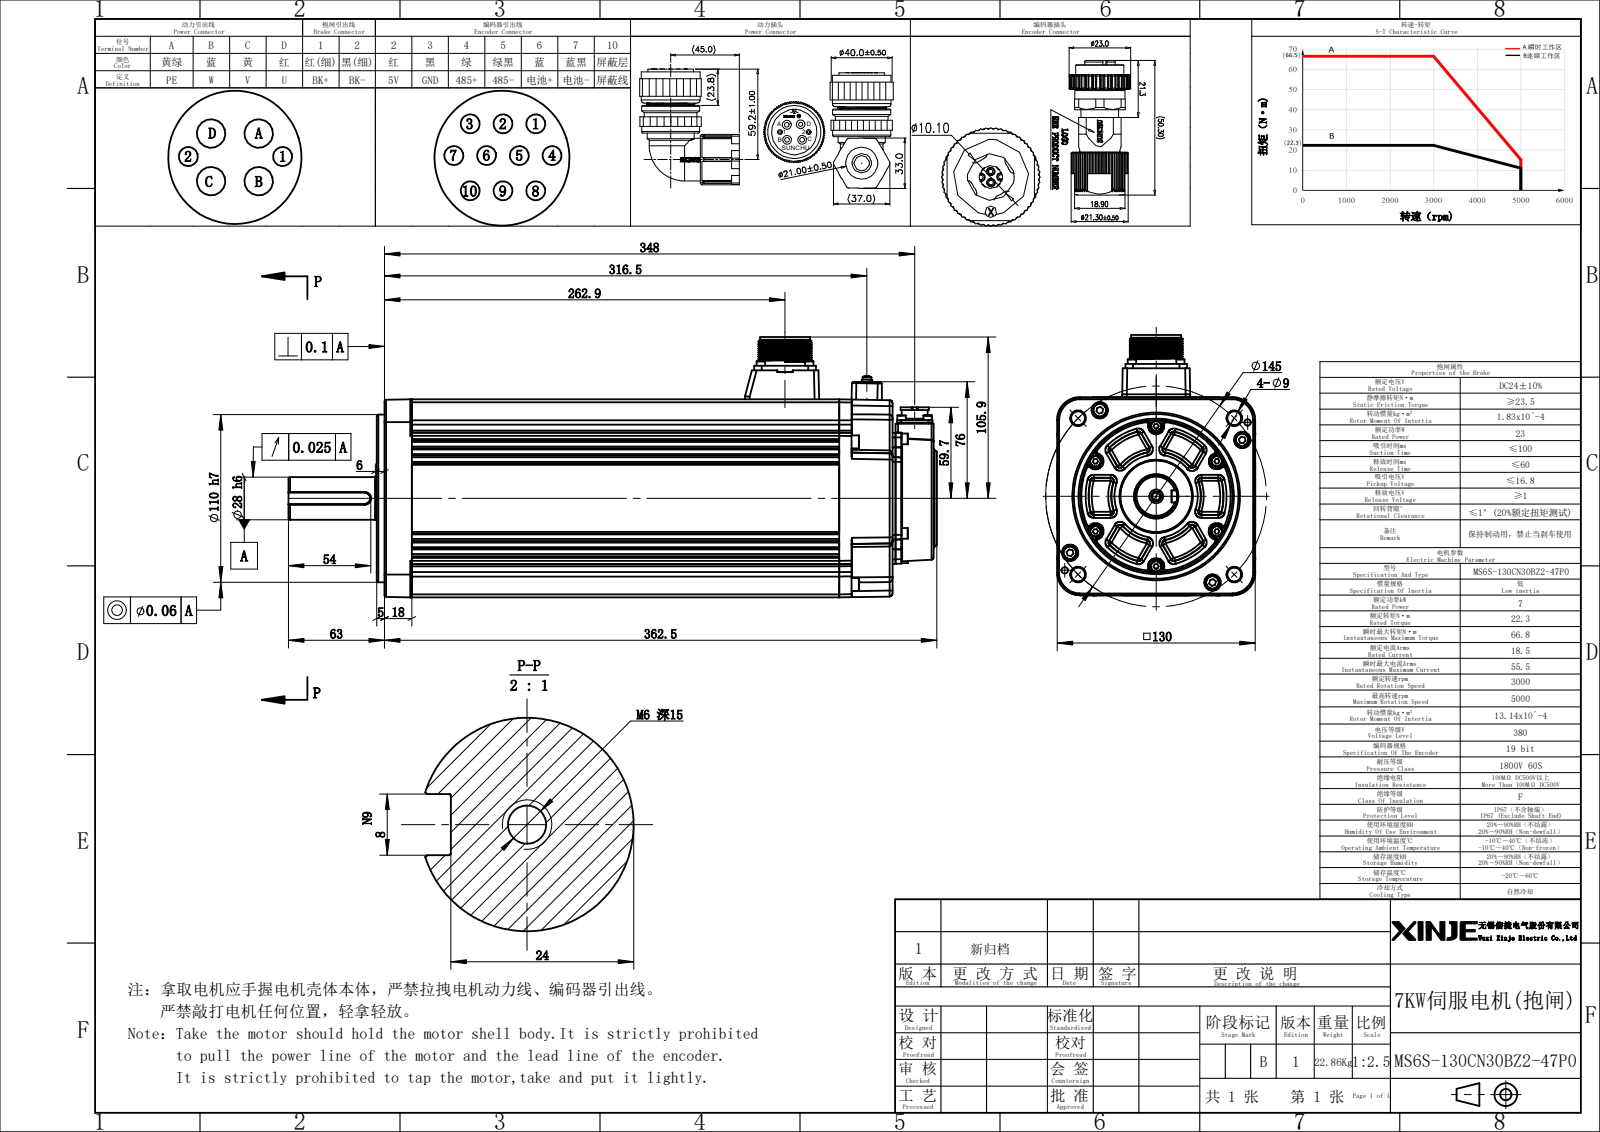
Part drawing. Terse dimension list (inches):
name: MS6S-130CN30BZ2-47P0
written by: SolidWorks 2022 (CONFIG_CONTROL_DESIGN)
unit: in
bodies: 53 solids, 3480 faces (1530 planar, 856 cylindrical, 1094 other)
size: 16.752 × 6.74 × 5.141
volume: 340.8 in³; area: 676.2 in²
holes: 10× ⌀0.04, 8× ⌀0.13, 7× ⌀0.126, 6× ⌀0.165, 4× ⌀0.138, 4× ⌀0.146, 4× ⌀0.157, 4× ⌀0.177, 4× ⌀0.215, 4× ⌀0.228, 3× ⌀0.197, 2× ⌀0.078
bosses: 12× ⌀0.276, 11× ⌀0.118, 10× ⌀0.157, 10× ⌀0.059, 10× ⌀0.03, 9× ⌀0.217, 4× ⌀0.354, 4× ⌀0.335
rounds: 67× R0.039, 44× R0.079, 32× R0.012, 26× R0.157, 20× R0.118, 17× R0.008, 12× R0.098, 8× R0.059
face distances: 5.118, 11.043, 0.079, 0.689, 11.732, 0.709, 0.02, 0.197, 11.752, 1.063
hole spacings: 0.097, 0.165, 0.094, 1.783, 2.461, 2.659, 3.27, 3.8
